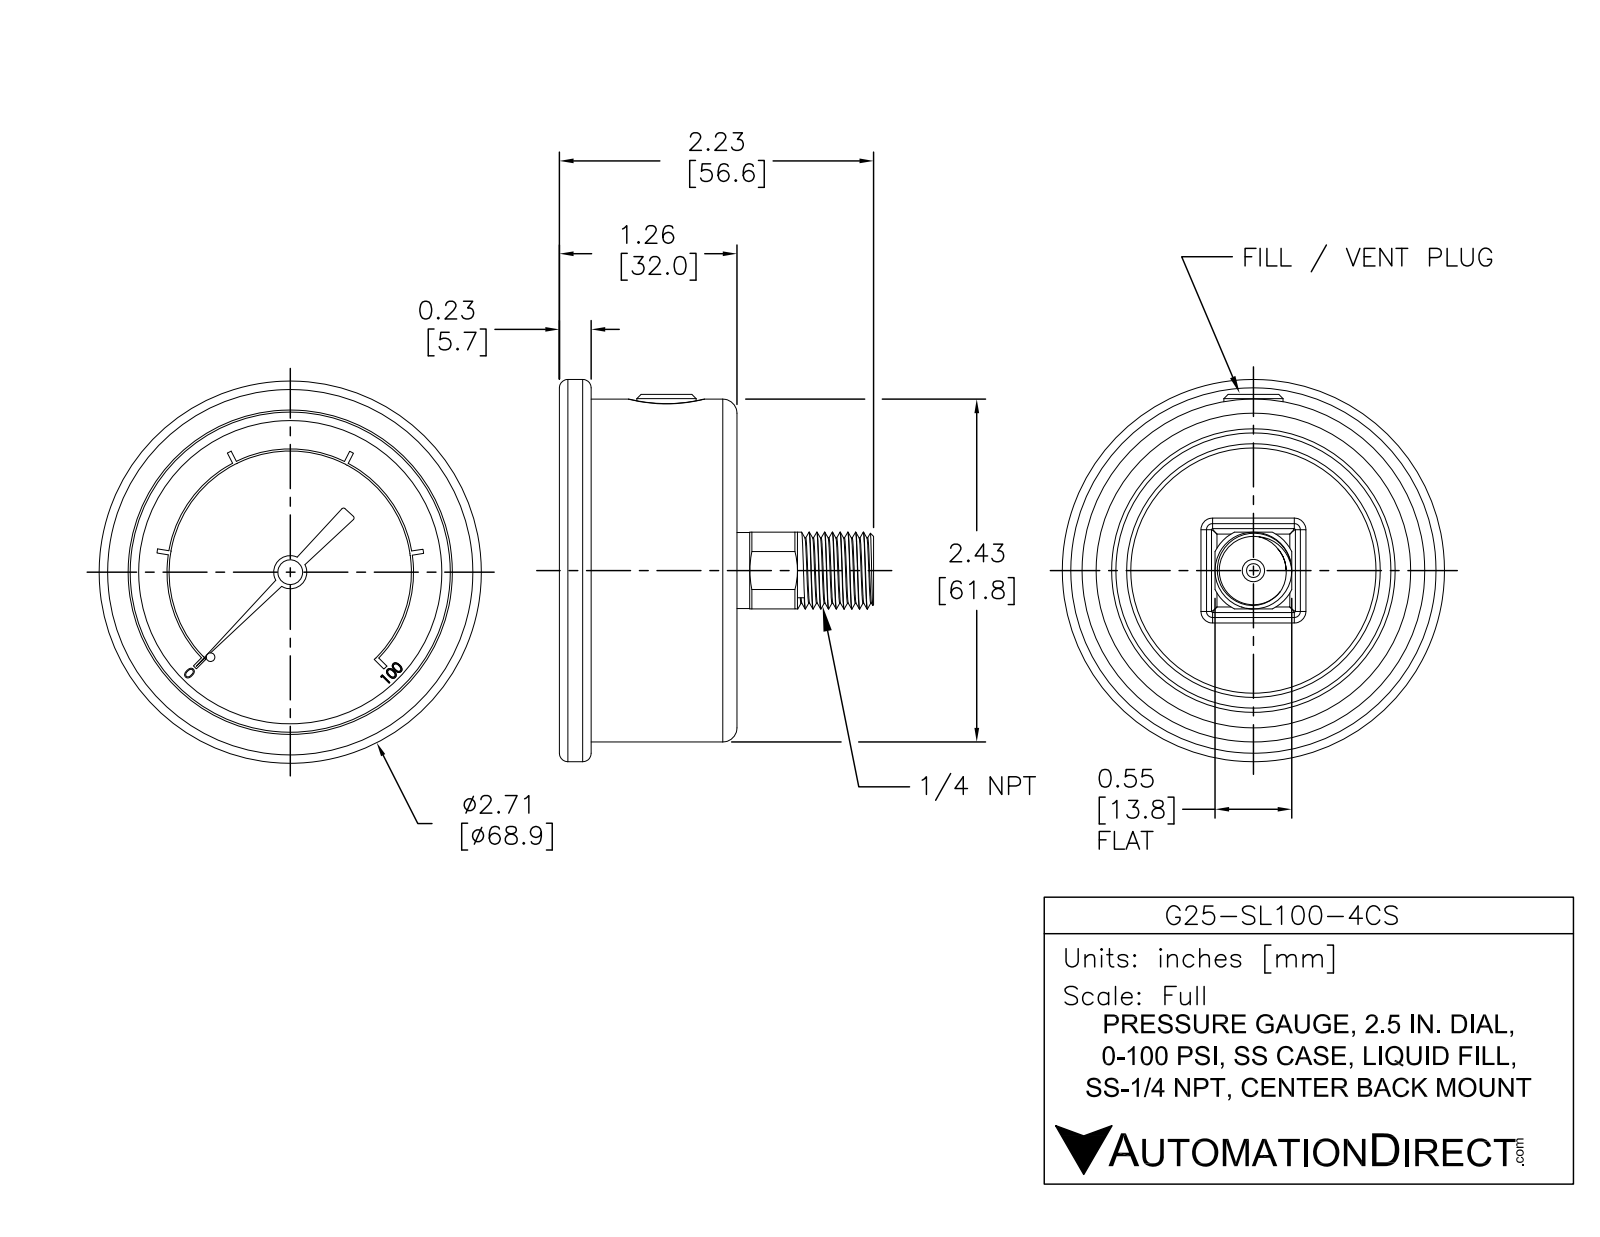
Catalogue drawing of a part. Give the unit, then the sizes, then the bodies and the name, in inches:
Units: inches
Overall size (bounding box): 2.713 × 2.713 × 2.23
Round holes (diameter × count): ⌀0.071 ×1, ⌀0.098 ×1, ⌀2.272 ×1
Round bosses / shafts (diameter × count): ⌀2.713 ×1, ⌀2.433 ×1, ⌀0.545 ×1, ⌀0.54 ×1, ⌀0.42 ×1, ⌀0.235 ×1, ⌀0.176 ×1, ⌀0.14 ×1
Partial cylindrical surfaces — rounded edges, fillets, slot ends (radius × count): R0.06 ×8, R0.015 ×2, R0.304 ×1, R0.86 ×1, R0.875 ×1
Main face-to-face distances: 0.95, 1.2, 0.25, 0.06, 1.01, 1.26, 1.035, 0.975, 0.025, 0.225
Volume: 5.168 in³ · Surface area: 24.82 in²
Bodies: 1 solid, 348 faces (208 planar, 83 cylindrical, 57 other)
Part name (STEP PRODUCT): G25-SL100-4CS
STEP written by: SolidWorks 2021 (AUTOMOTIVE_DESIGN)
